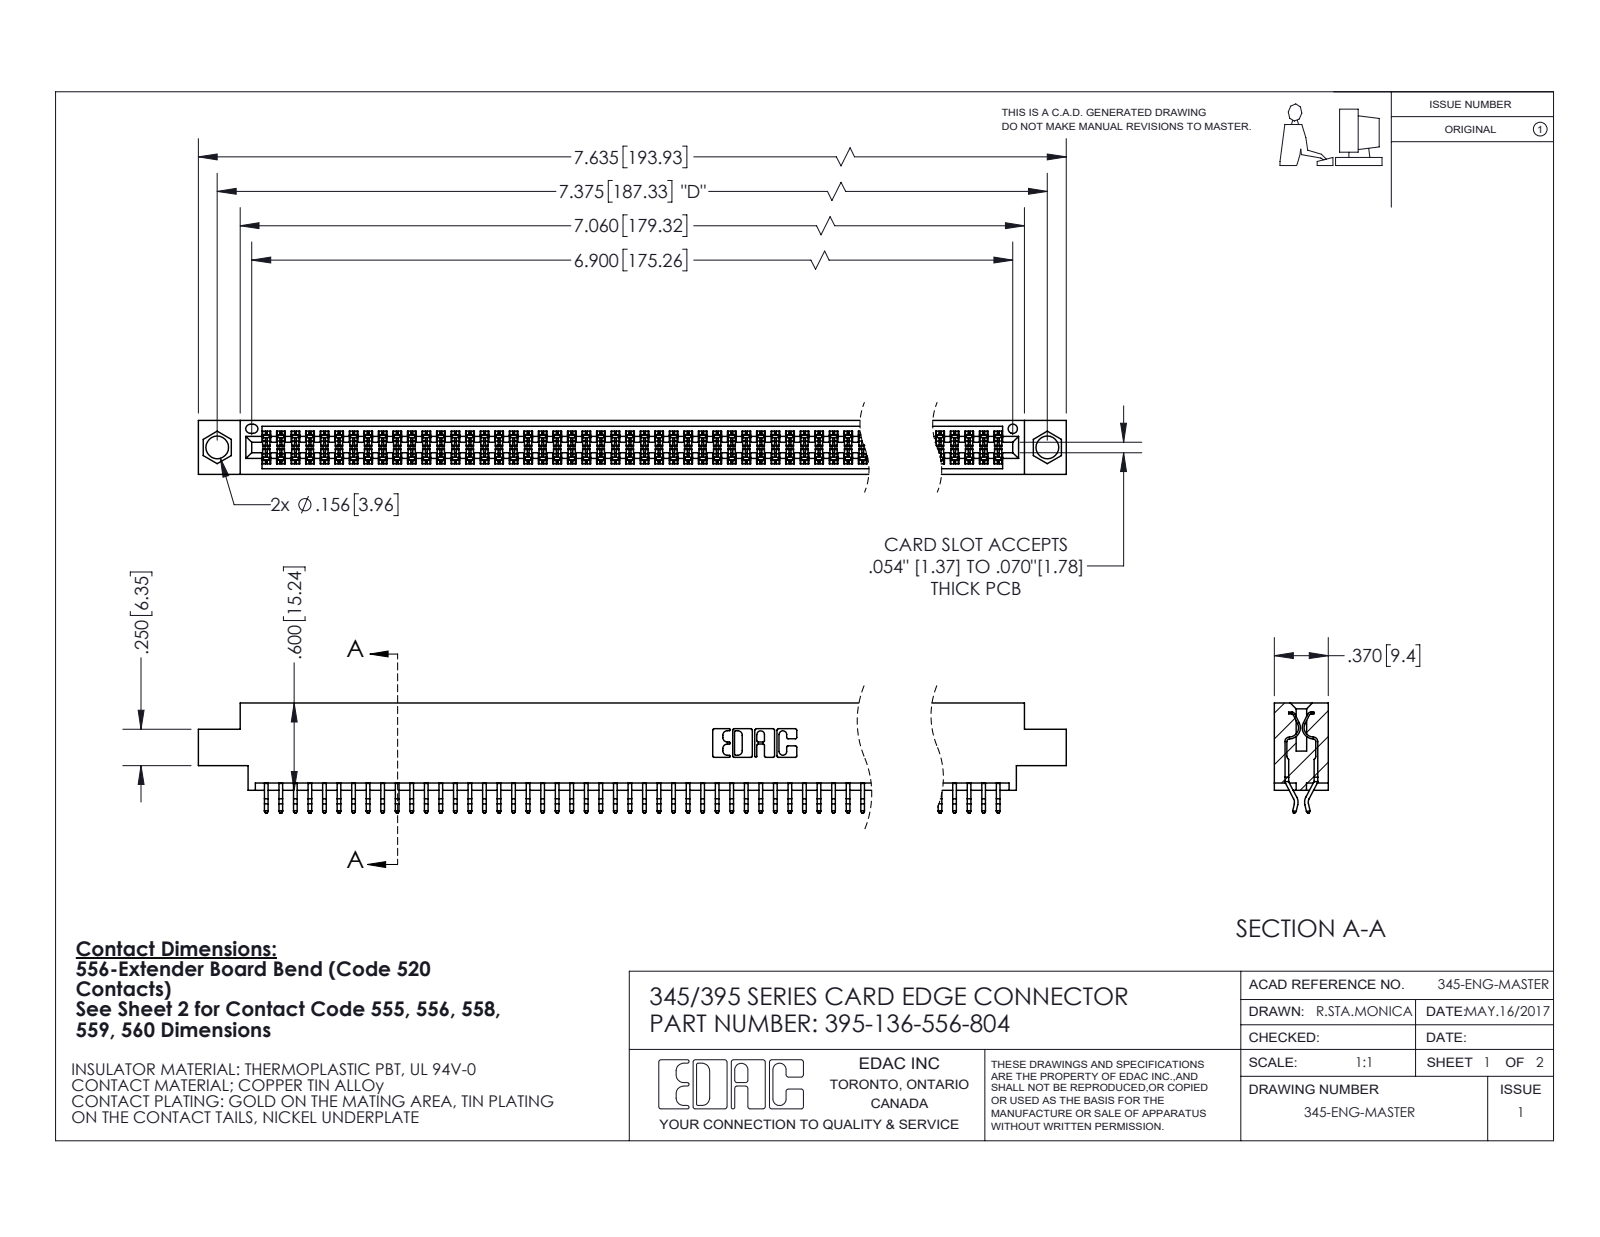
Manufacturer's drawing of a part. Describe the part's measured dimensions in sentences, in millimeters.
The part is named "395-136-556-804; 345 Part_0.170 Offset - 0.156 Dia-TI; 345-292-001_556 Tail". Its 3-D file was written by "SolidWorks 2020 (CONFIG_CONTROL_DESIGN)". It is 137 solids with 7760 faces: 5130 planar, 2630 cylindrical and 0 other. Overall it measures 193.9 by 19.2 by 9.4 millimeters. Its volume is 18 860 cubic millimeters and its surface area 28 250 square millimeters. Round holes: 2 of diameter 4, 1 of diameter 1.6. Partial cylindrical surfaces (rounded edges, fillets, slot ends): 272 of radius 0.2, 22 of radius 0.3, 6 of radius 0.2, 6 of radius 0.8, 3 of radius 0.7, 2 of radius 0.3, 2 of radius 0.4, 2 of radius 0.5. The main face-to-face distances are 1.8, 7.6, 9.4, 5.1, 0.6, 2.5, 6.9, 5.7, 4.4, 3.8. The hole center spacings are 6.9, 181.3, 187.3.
